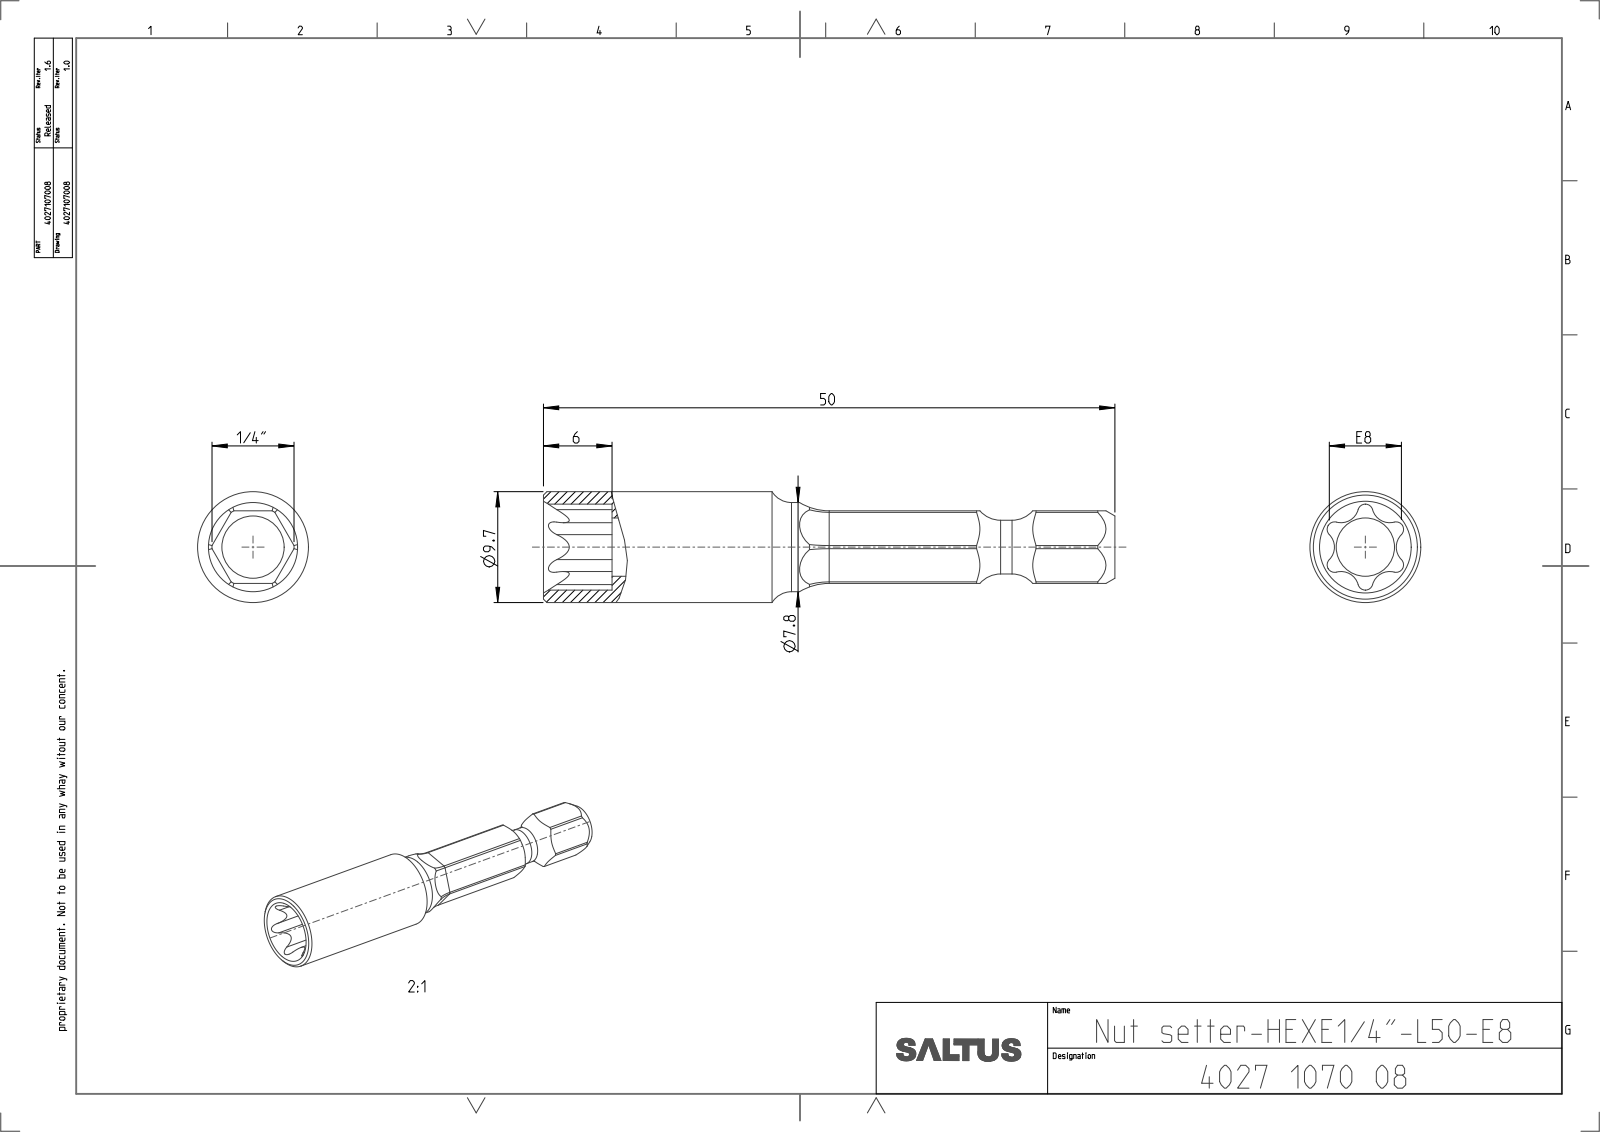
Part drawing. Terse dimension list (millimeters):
name: 4027107008
written by: CREO PARAMETRIC BY PTC INC, 2022414 (CONFIG_CONTROL_DESIGN)
unit: mm
bodies: 1 solid, 73 faces (15 planar, 38 cylindrical, 20 other)
size: 50 × 9.7 × 9.7
volume: 2 109 mm³; area: 1 642 mm²
holes: 1× ⌀5.1
bosses: 1× ⌀9.7, 1× ⌀7.8, 1× ⌀4.7
rounds: 6× R0.66, 6× R1.55, 6× R5, 1× R3.59
face distances: 6.34, 6.36, 50, 44, 6
